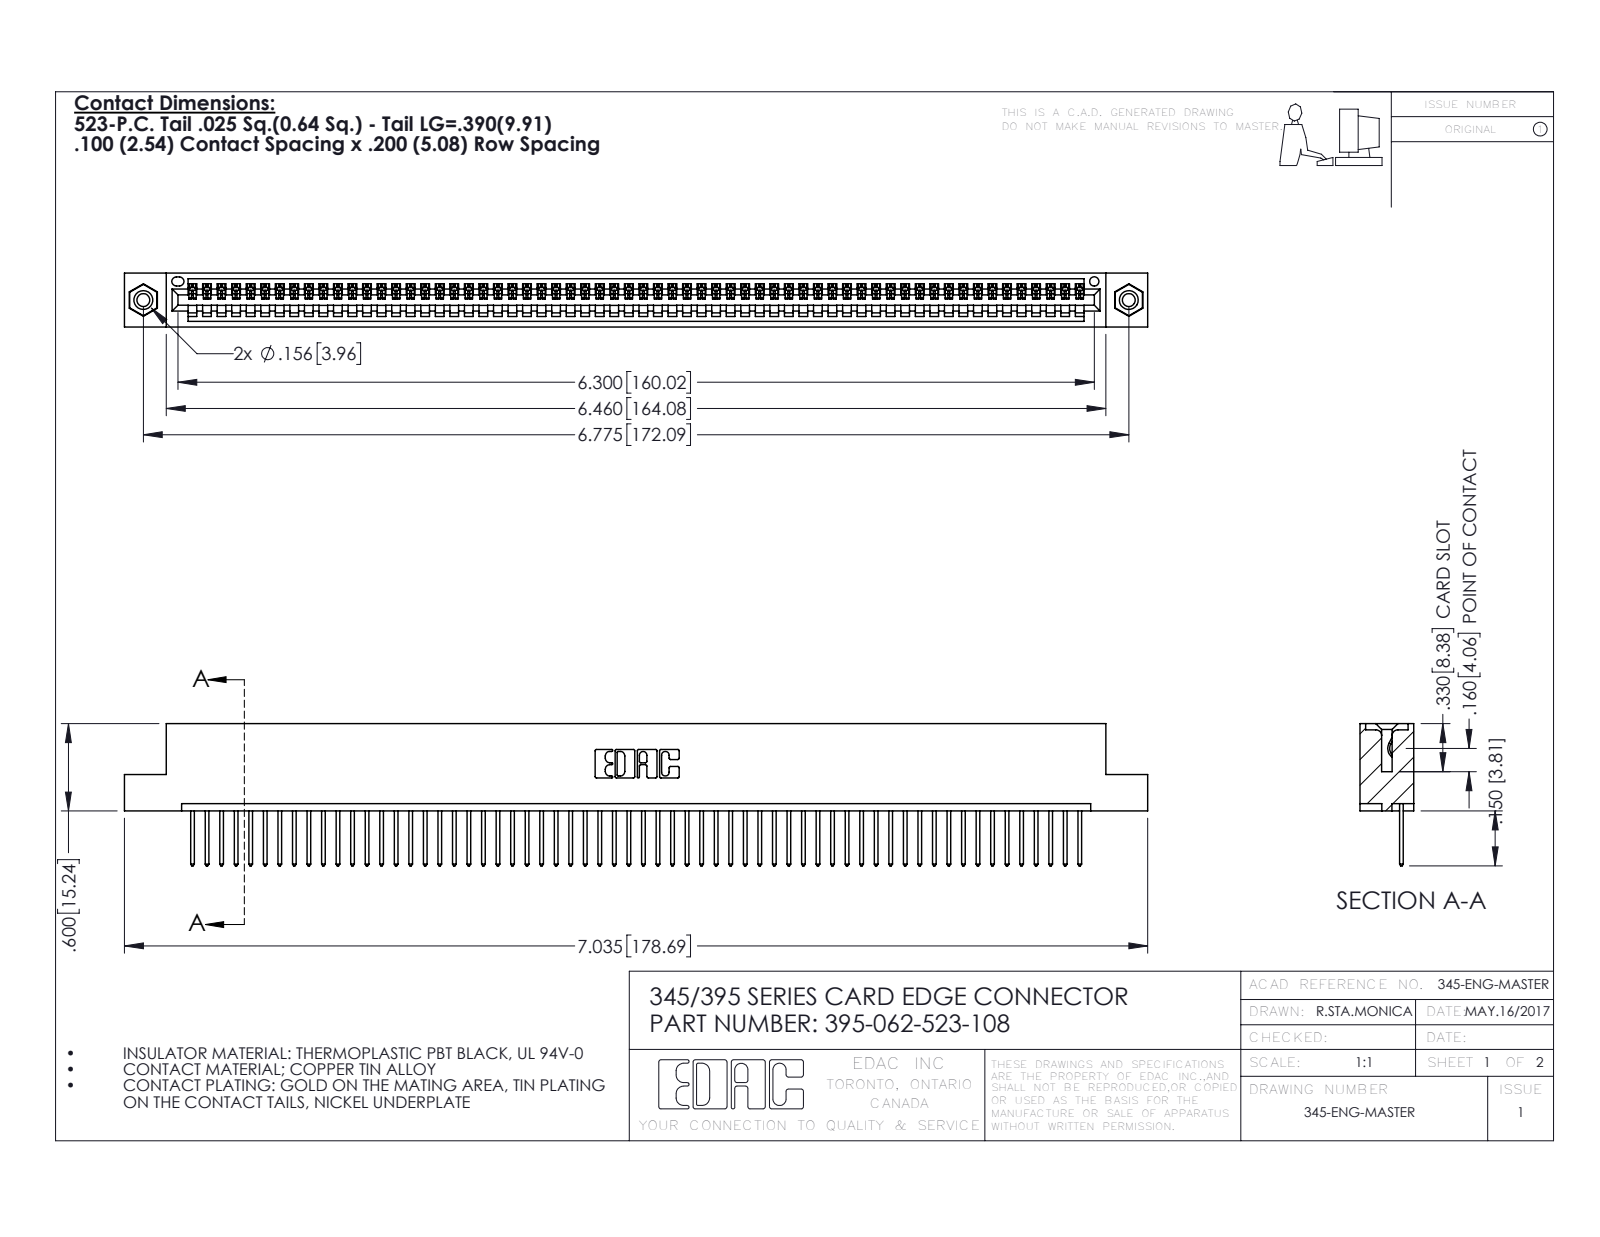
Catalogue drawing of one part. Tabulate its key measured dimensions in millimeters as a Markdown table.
| quantity | value |
| --- | --- |
| part name | 345-292-001_345-293-123; 345 Part_Flush Mounting Lugs - 0.156 Dia-TI; 345-250-001_345-250-003-102; 395-062-523-108 |
| STEP written by | SolidWorks 2016 (CONFIG_CONTROL_DESIGN) |
| units | millimeters |
| bodies | 65 solids, 3782 faces (2592 planar, 1174 cylindrical, 16 other) |
| overall size | 178.7 × 24.8 × 9.4 |
| volume | 17 110 mm³ |
| surface area | 23 090 mm² |
| round holes (diameter × count) | 2.3 × 2, 3.2 × 2, 4 × 2, 1.6 × 1 |
| round bosses / shafts (diameter × count) | 3.9 × 2 |
| partial cylindrical surfaces (radius × count) | 0.2 × 124, 0.3 × 124, 0.3 × 22, 0.2 × 6, 0.8 × 6, 0.7 × 3, 0.8 × 2, 1 × 2 |
| main face-to-face distances | 1.8, 7.6, 9.4, 5.1, 2.5, 6.9, 0.6, 5.7, 3.8, 1.8 |
| hole center spacings | 6.9, 166.1, 172.1 |
